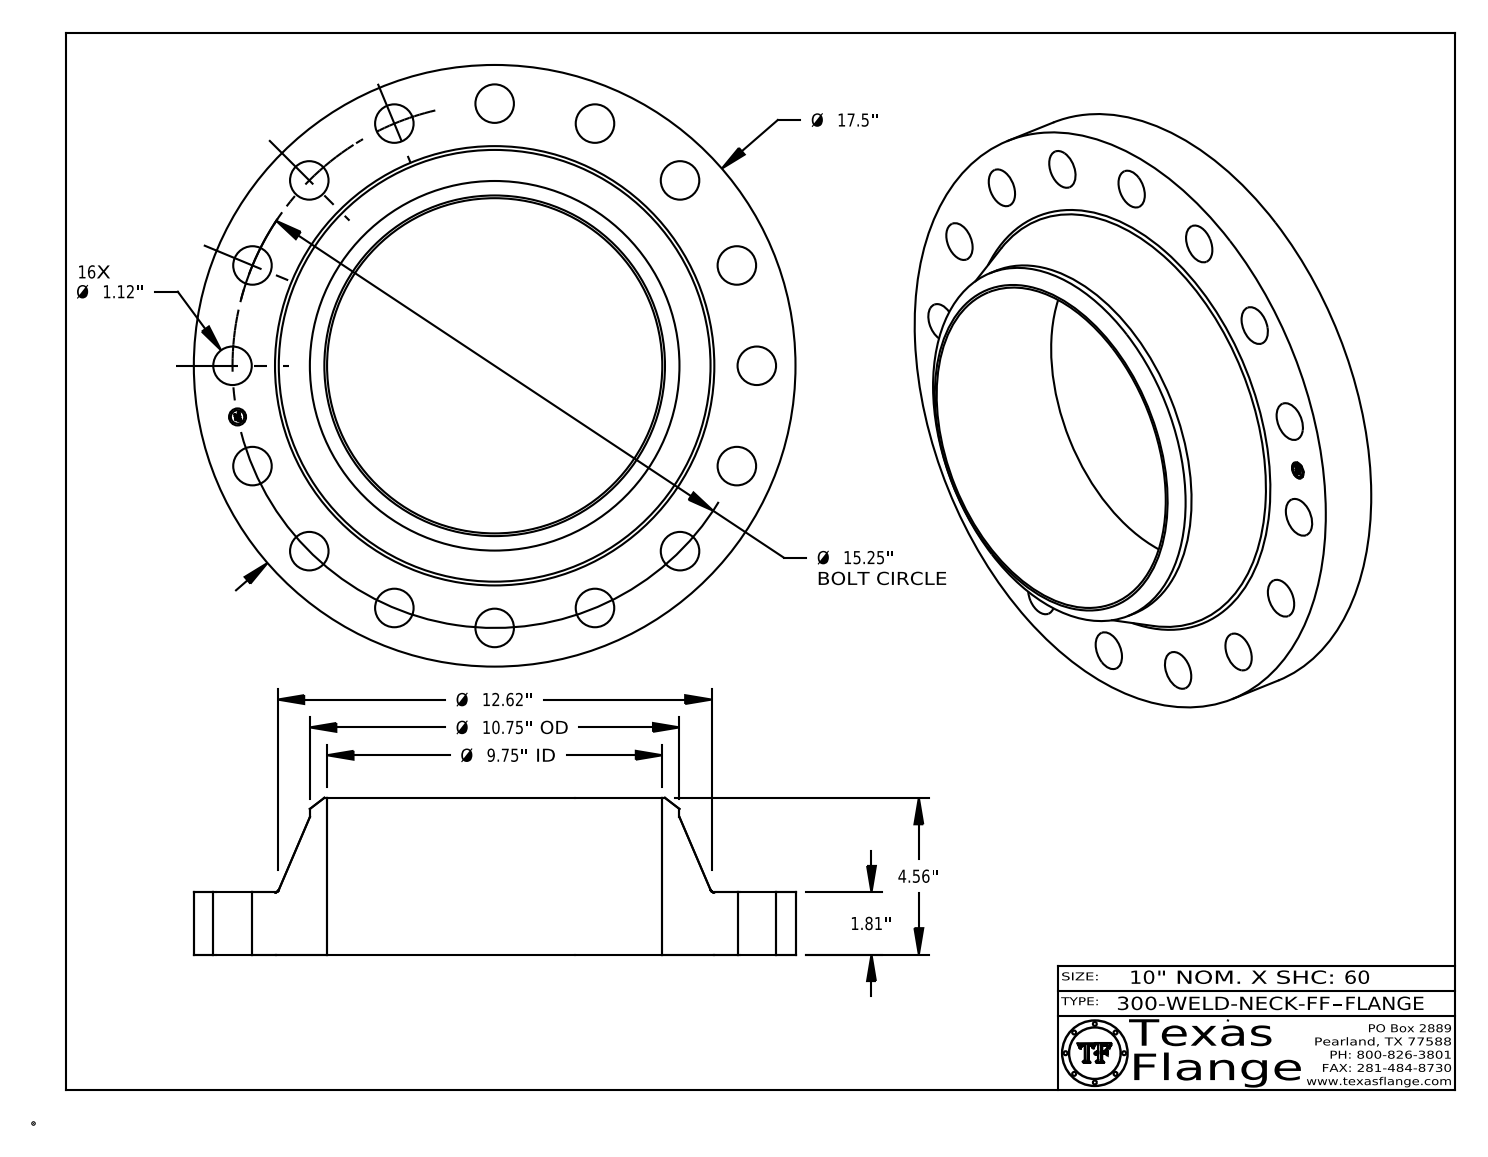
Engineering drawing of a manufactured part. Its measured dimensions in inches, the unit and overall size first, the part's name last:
Units: inches
Overall size (bounding box): 17.5 × 17.5 × 4.56
Round holes (diameter × count): ⌀1.12 ×16, ⌀0.495 ×1, ⌀9.75 ×1
Round bosses / shafts (diameter × count): ⌀0.03 ×8, ⌀17.5 ×1, ⌀10.75 ×1, ⌀0.39 ×1
Main face-to-face distances: 1.81, 4.56, 2.75, 0.015, 1.795, 2.765, 0.148, 0.145, 0.027, 0.096
Hole centre spacings: 8.472, 10.783, 14.957, 14.089, 7.625, 2.975, 2.975, 5.836
Volume: 350.4 in³ · Surface area: 705.3 in²
Bodies: 1 solid, 433 faces (369 planar, 58 cylindrical, 6 other)
Part name (STEP PRODUCT): 300-WELD-NECK-FF
STEP written by: CATIA V5 STEP AP214 (AUTOMOTIVE_DESIGN)
